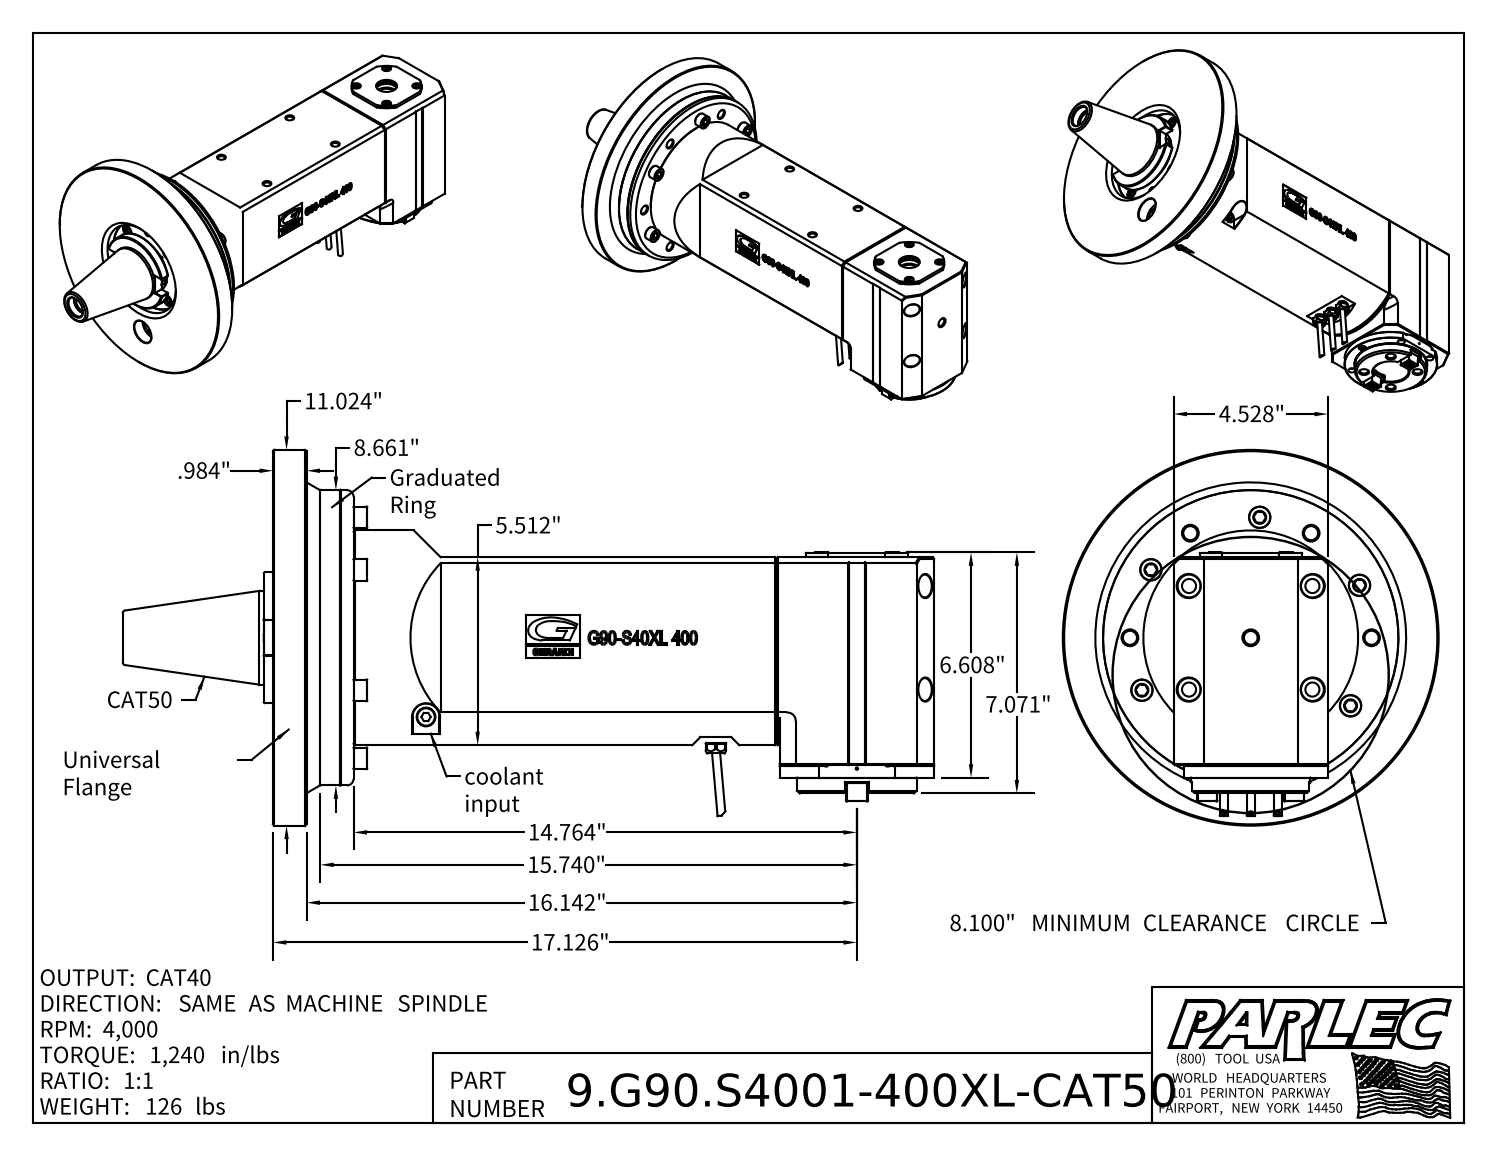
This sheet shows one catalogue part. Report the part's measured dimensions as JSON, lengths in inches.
{"part_name": "9.G90.S4001-400XL-CAT50; 9_G90_S40XL_400; 9_SK_45_1 (Classic, Cat50, MTC); 9_UF_00005 (Clas", "step_written_by": "Autodesk Inventor 2025 (AUTOMOTIVE_DESIGN)", "units": "inches", "bodies": {"solids": 23, "faces": 2191, "planar": 850, "cylindrical": 507, "other": 834}, "overall_size": [23.799, 11.024, 11.024], "volume_in3": 495.5, "surface_area_in2": 1585, "round_holes": [[0.335, 20], [0.268, 12], [0.354, 12], [0.413, 11], [0.197, 10], [0.394, 10], [0.551, 10], [0.165, 6], [0.217, 6], [0.13, 5], [0.346, 5], [0.433, 5]], "round_bosses_or_shafts": [[0.63, 6], [0.512, 4], [0.386, 4], [0.315, 4], [0.236, 4], [0.394, 3], [3.504, 2], [2.165, 2]], "partial_cylinders_radius": [[0.02, 48], [0.118, 36], [0.394, 7], [0.512, 6], [0.531, 6], [1.083, 5], [0.325, 3], [0.201, 2]], "face_to_face_distances": [1.378, 0.394, 4.528, 0.984, 0.787, 0.591, 1.772, 2.362, 19.39, 18.799], "hole_center_spacings": [1.969, 2.362, 5.148, 3.105, 3.125, 3.543, 5.054, 0.787]}
